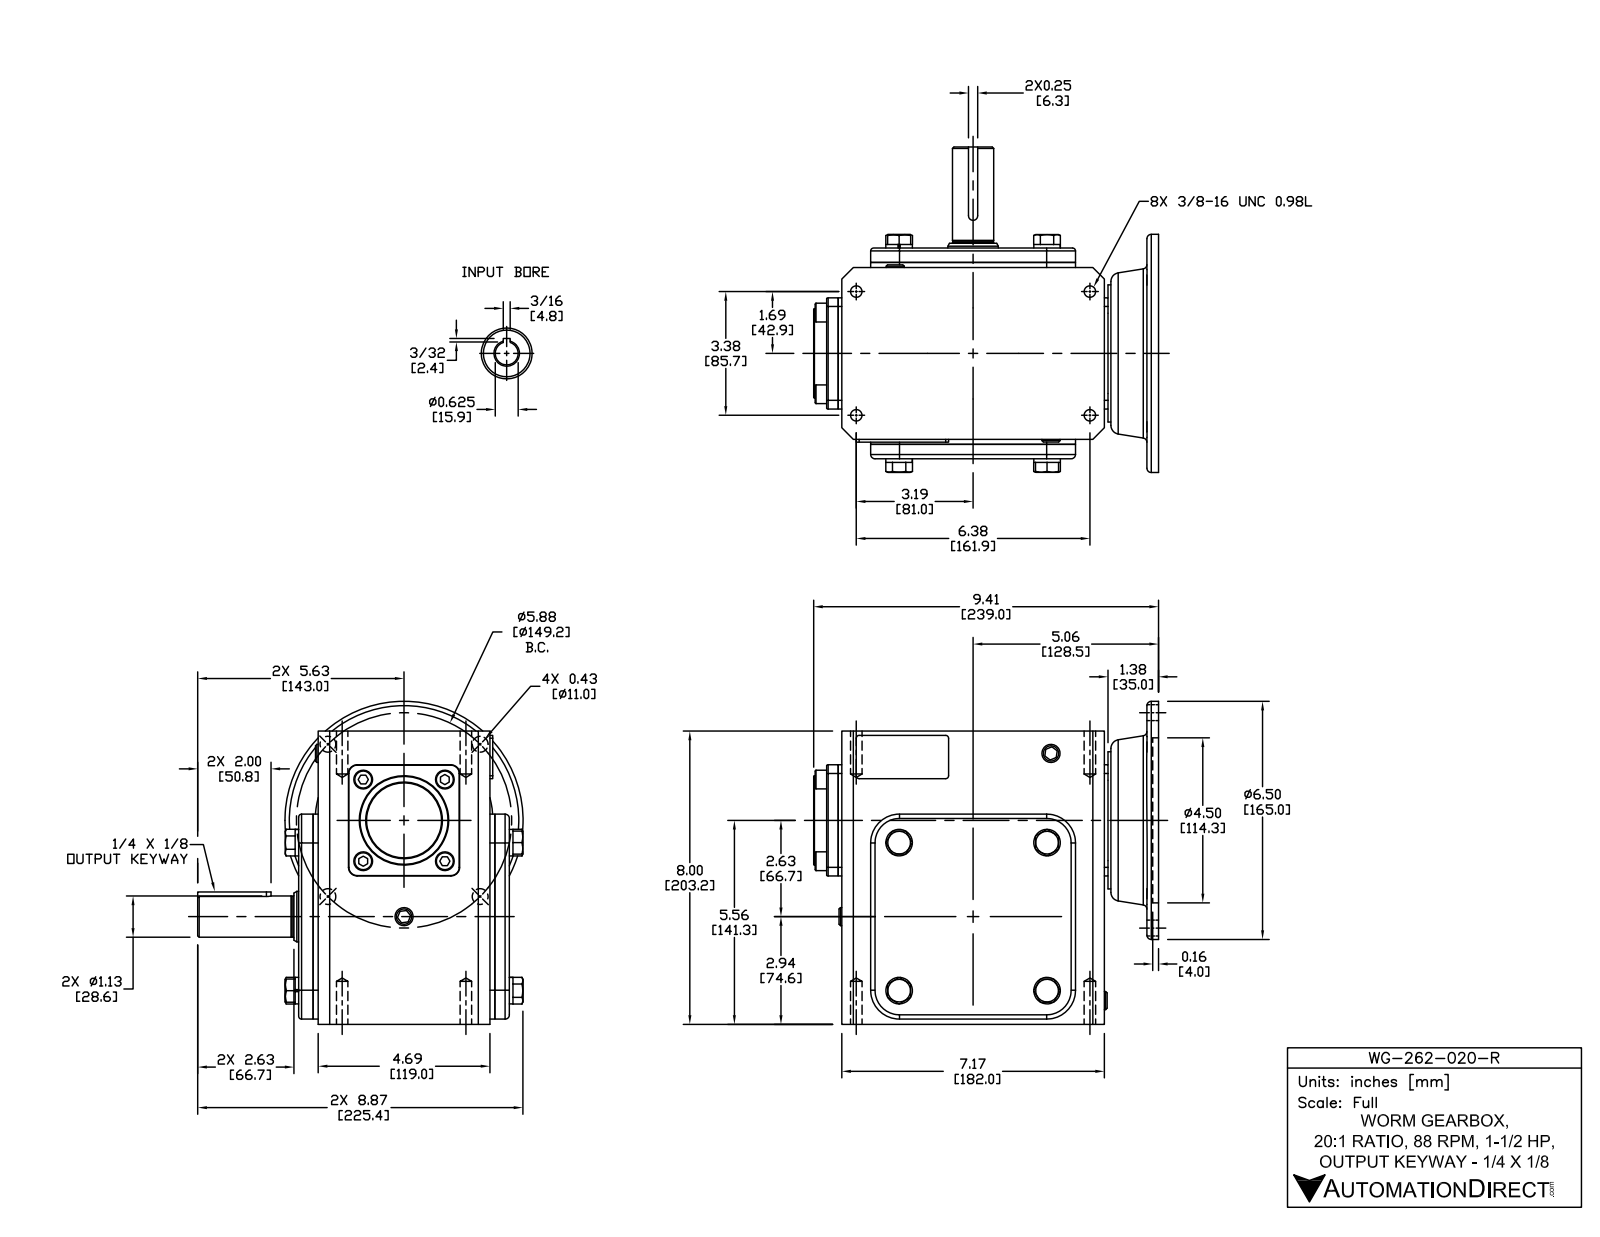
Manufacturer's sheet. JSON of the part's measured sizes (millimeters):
{"part_name": "WG-262-020-R", "step_written_by": "SolidWorks 2015 (CONFIG_CONTROL_DESIGN)", "units": "millimeters", "bodies": {"solids": 37, "faces": 527, "planar": 293, "cylindrical": 138, "other": 96}, "overall_size": [239, 225.5, 223.8], "volume_mm3": 5213000, "surface_area_mm2": 395900, "round_holes": [[8, 4], [10.3, 4], [15, 1], [15.9, 1], [30, 1], [35, 1], [37, 1], [50, 1], [97, 1], [114.3, 1]], "round_bosses_or_shafts": [[18.4, 4], [13, 4], [165, 1], [62, 1], [52, 1], [29, 1], [28.6, 1], [28.3, 1]], "partial_cylinders_radius": [[2, 12], [3, 4], [6, 4], [20, 4], [0.5, 2], [1, 2], [3.2, 1]], "face_to_face_distances": [10, 126, 136, 132.5, 13.5, 3.5, 122.5, 203.2, 2.5, 184.5], "hole_center_spacings": [74.6, 105.5, 54.6, 85.7, 130.6, 149.2, 161.9, 183.2]}
